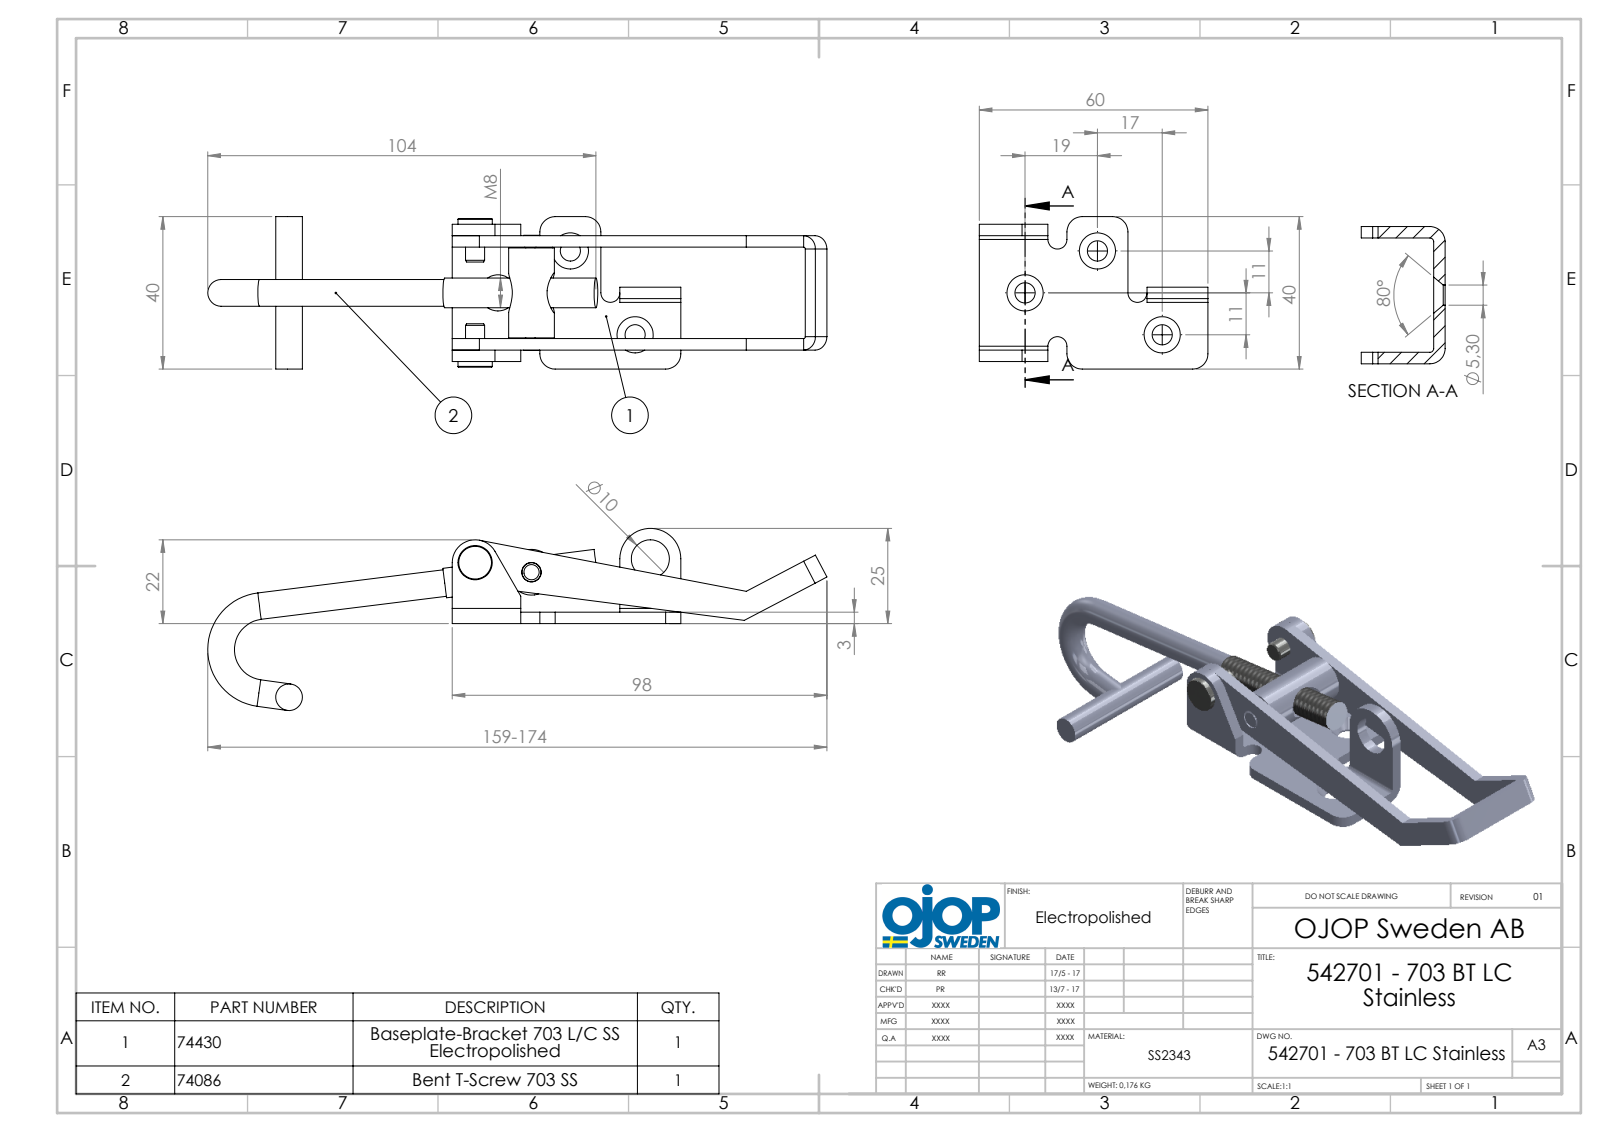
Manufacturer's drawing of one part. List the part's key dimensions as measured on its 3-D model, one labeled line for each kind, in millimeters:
Part name (STEP PRODUCT): 703 - Rulle RF; 542701 - 703 BT LC Stainless; 703 - Platta LC RF; 704 - Rivet Gradin (+2 more)
STEP written by: SolidWorks 2015 (AUTOMOTIVE_DESIGN)
Units: millimetres
Bodies: 6 solids, 159 faces (66 planar, 73 cylindrical, 20 other)
Overall size (bounding box): 167.62 × 40.05 × 32.35
Volume: 22 625 mm³ · Surface area: 17 386 mm²
Round holes (diameter × count): ⌀5.3 ×3, ⌀5.1 ×2, ⌀7.2 ×2, ⌀10 ×1
Round bosses / shafts (diameter × count): ⌀7 ×4, ⌀5 ×2, ⌀12 ×1, ⌀9 ×1, ⌀7.8 ×1
Partial cylindrical surfaces — rounded edges, fillets, slot ends (radius × count): R4 ×7, R1 ×3, R2.5 ×3, R0.5 ×2, R3.5 ×2, R6 ×1, R8 ×1
Main face-to-face distances: 3, 27, 30, 16.5, 13.5, 24, 6, 33, 19.5, 10.5
Hole centre spacings: 15.02, 21.95, 27.8, 31.38, 37.64, 46.01
